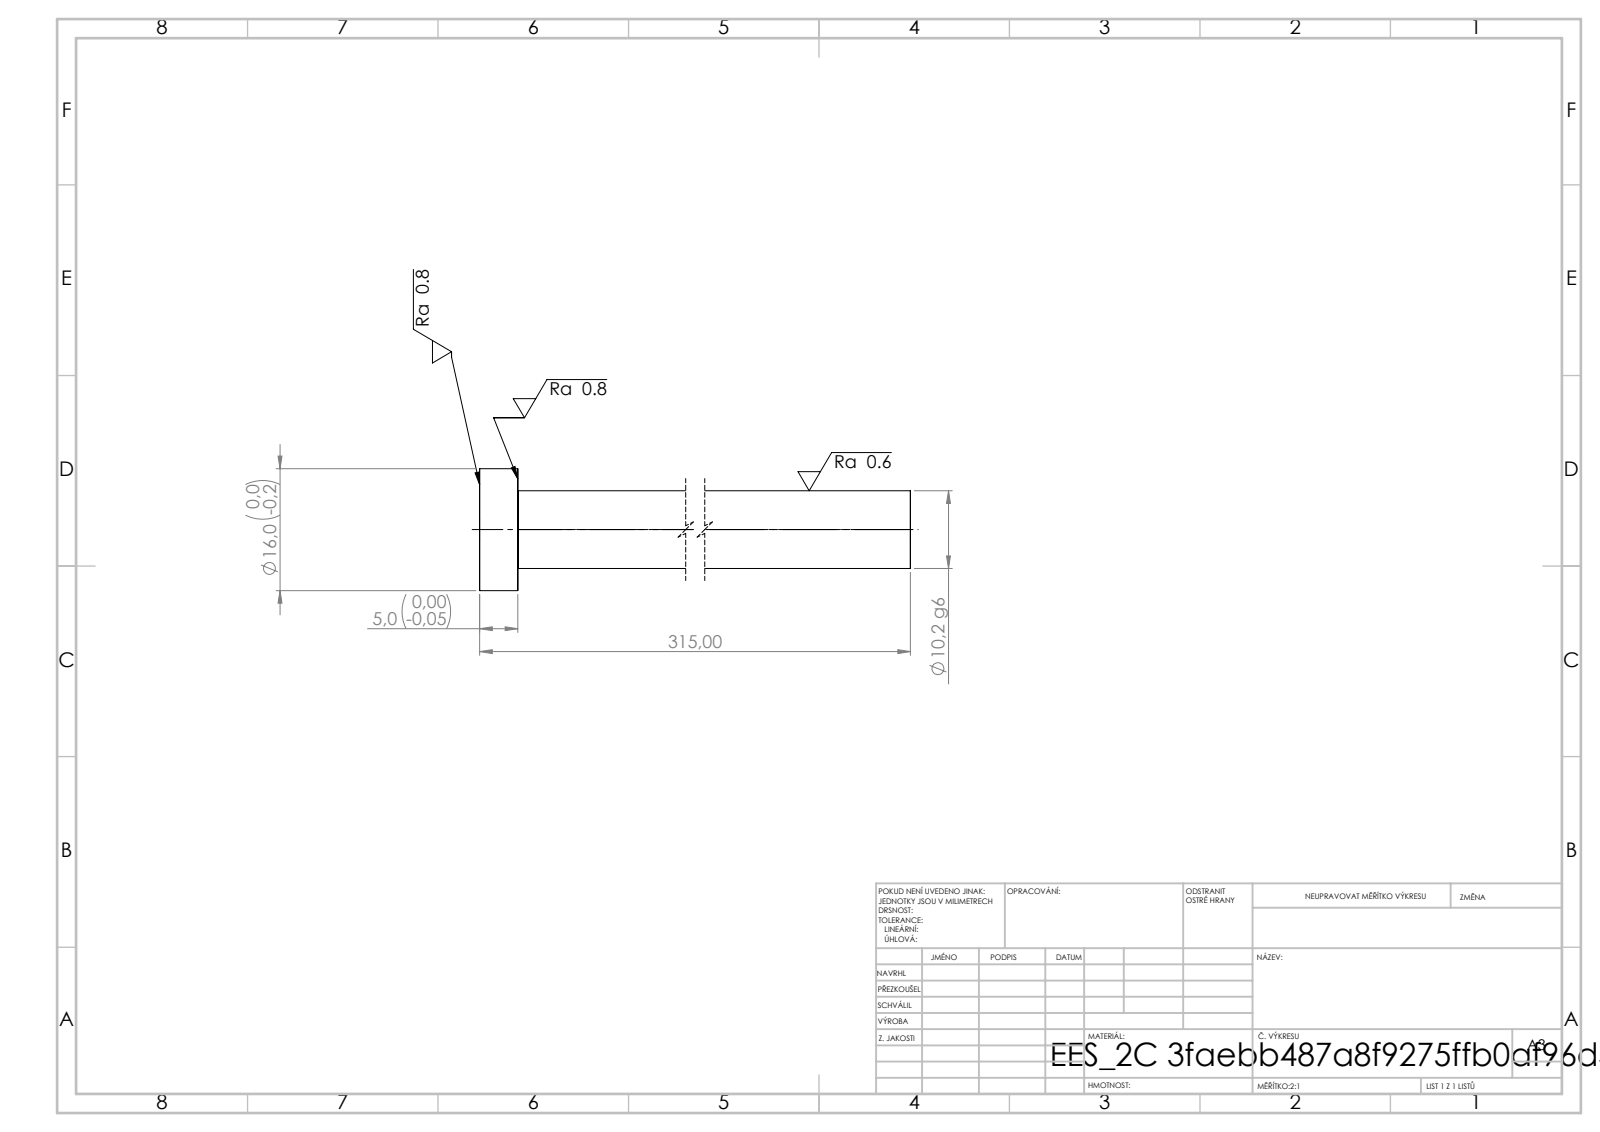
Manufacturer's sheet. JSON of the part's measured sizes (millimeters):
{"step_written_by": "SolidWorks 2019 (CONFIG_CONTROL_DESIGN)", "units": "millimeters", "bodies": {"solids": 1, "faces": 7, "planar": 3, "cylindrical": 4, "other": 0}, "overall_size": [315, 16, 16], "volume_mm3": 26336, "surface_area_mm2": 10587, "round_bosses_or_shafts": [[16, 1], [10.2, 1]], "face_to_face_distances": [5, 315, 310]}
